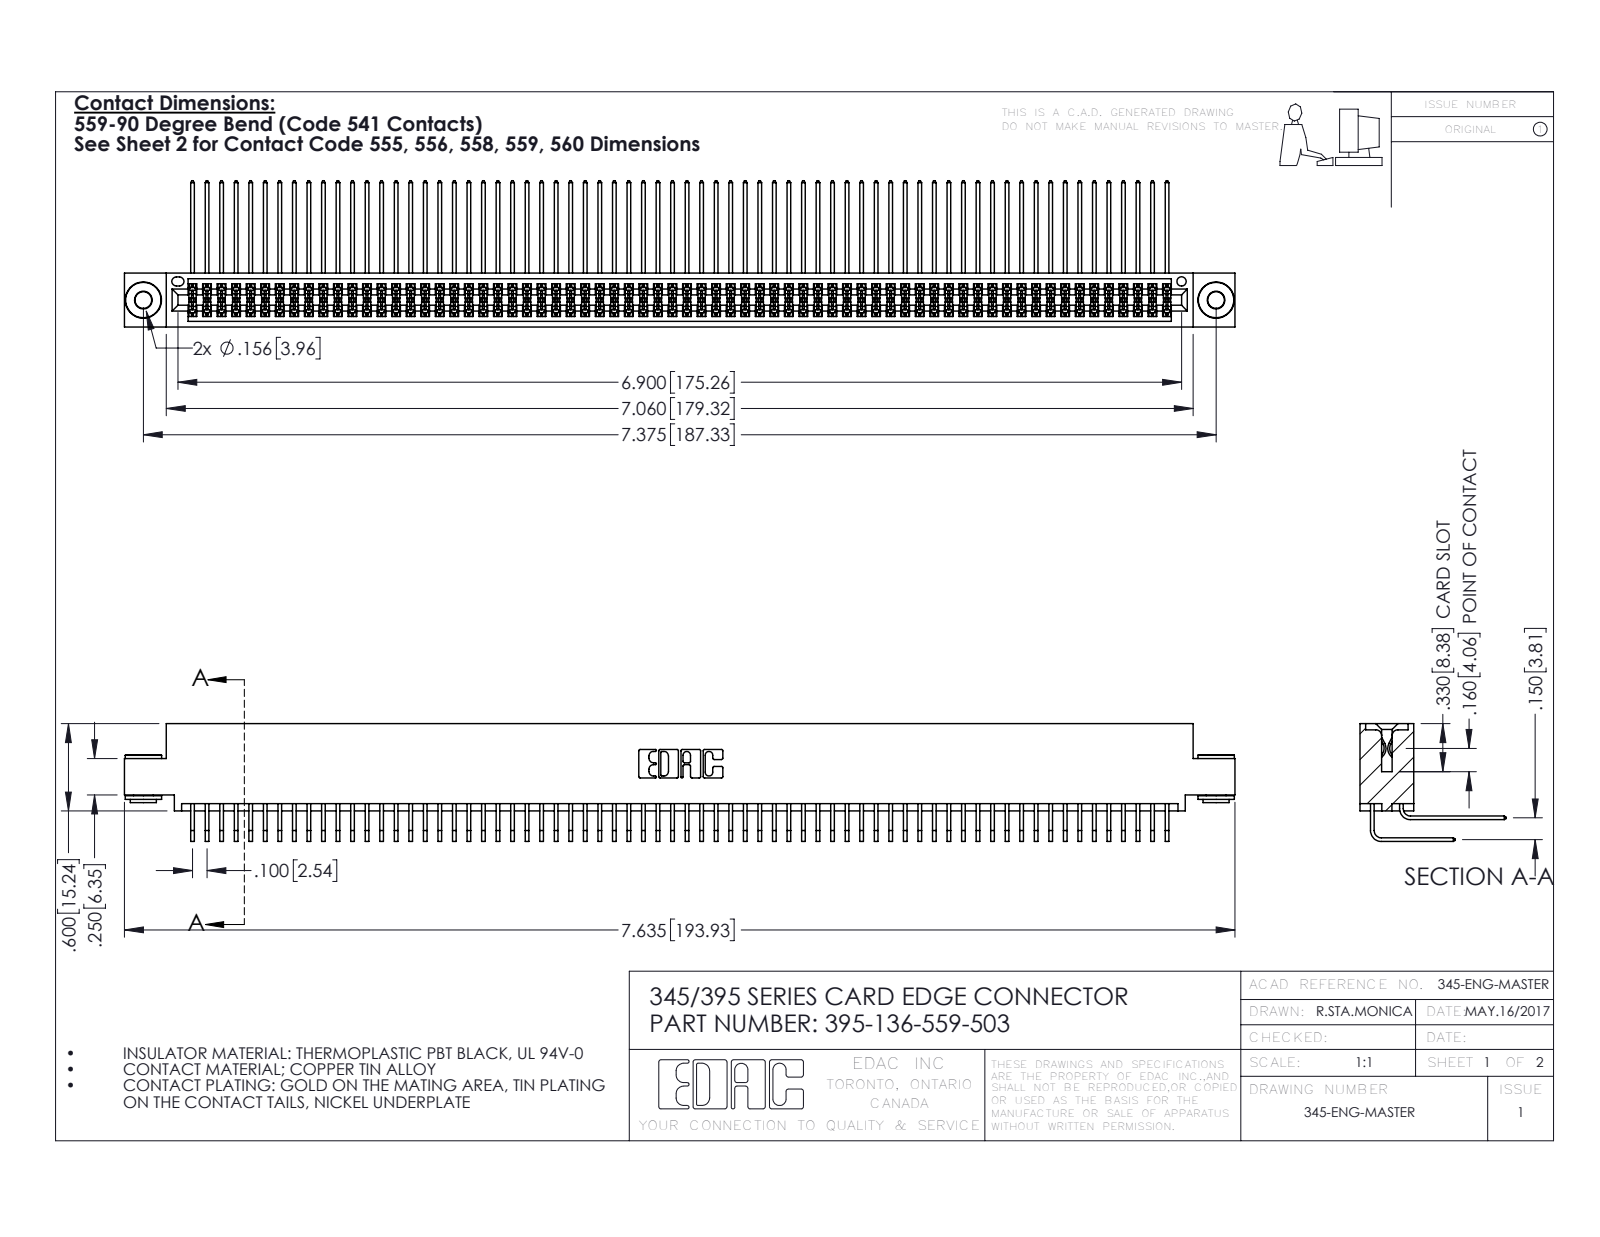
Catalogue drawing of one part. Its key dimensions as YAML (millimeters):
part_name: "345-250-002_345-250-002-102; 345 Part_0.110 Offset - 0.156 Dia-TH; 395-136-559-503; 345-292-001_559 Tail - 2 (+1 more)"
step_written_by: "SolidWorks 2016 (CONFIG_CONTROL_DESIGN)"
units: millimeters
bodies: {solids: 139, faces: 7240, planar: 4854, cylindrical: 2378, other: 8}
overall_size: [193.9, 25.5, 20.5]
volume: 19810
surface_area: 33770
round_holes:
  - {diameter: 2.9, count: 2}
  - {diameter: 4, count: 2}
  - {diameter: 1.6, count: 1}
round_bosses_or_shafts:
  - {diameter: 6.4, count: 2}
  - {diameter: 4.6, count: 2}
  - {diameter: 3.5, count: 2}
partial_cylinders:
  - {radius: 0.2, count: 271}
  - {radius: 0.3, count: 22}
  - {radius: 0.2, count: 6}
  - {radius: 0.8, count: 6}
  - {radius: 0.7, count: 3}
  - {radius: 0.4, count: 2}
  - {radius: 0.5, count: 2}
  - {radius: 0.6, count: 2}
face_to_face_distances: [1.8, 7.6, 5.1, 9.4, 0.6, 2.5, 6.9, 5.7, 4.4, 3.8]
hole_center_spacings: [6.9, 181.3, 187.3]
